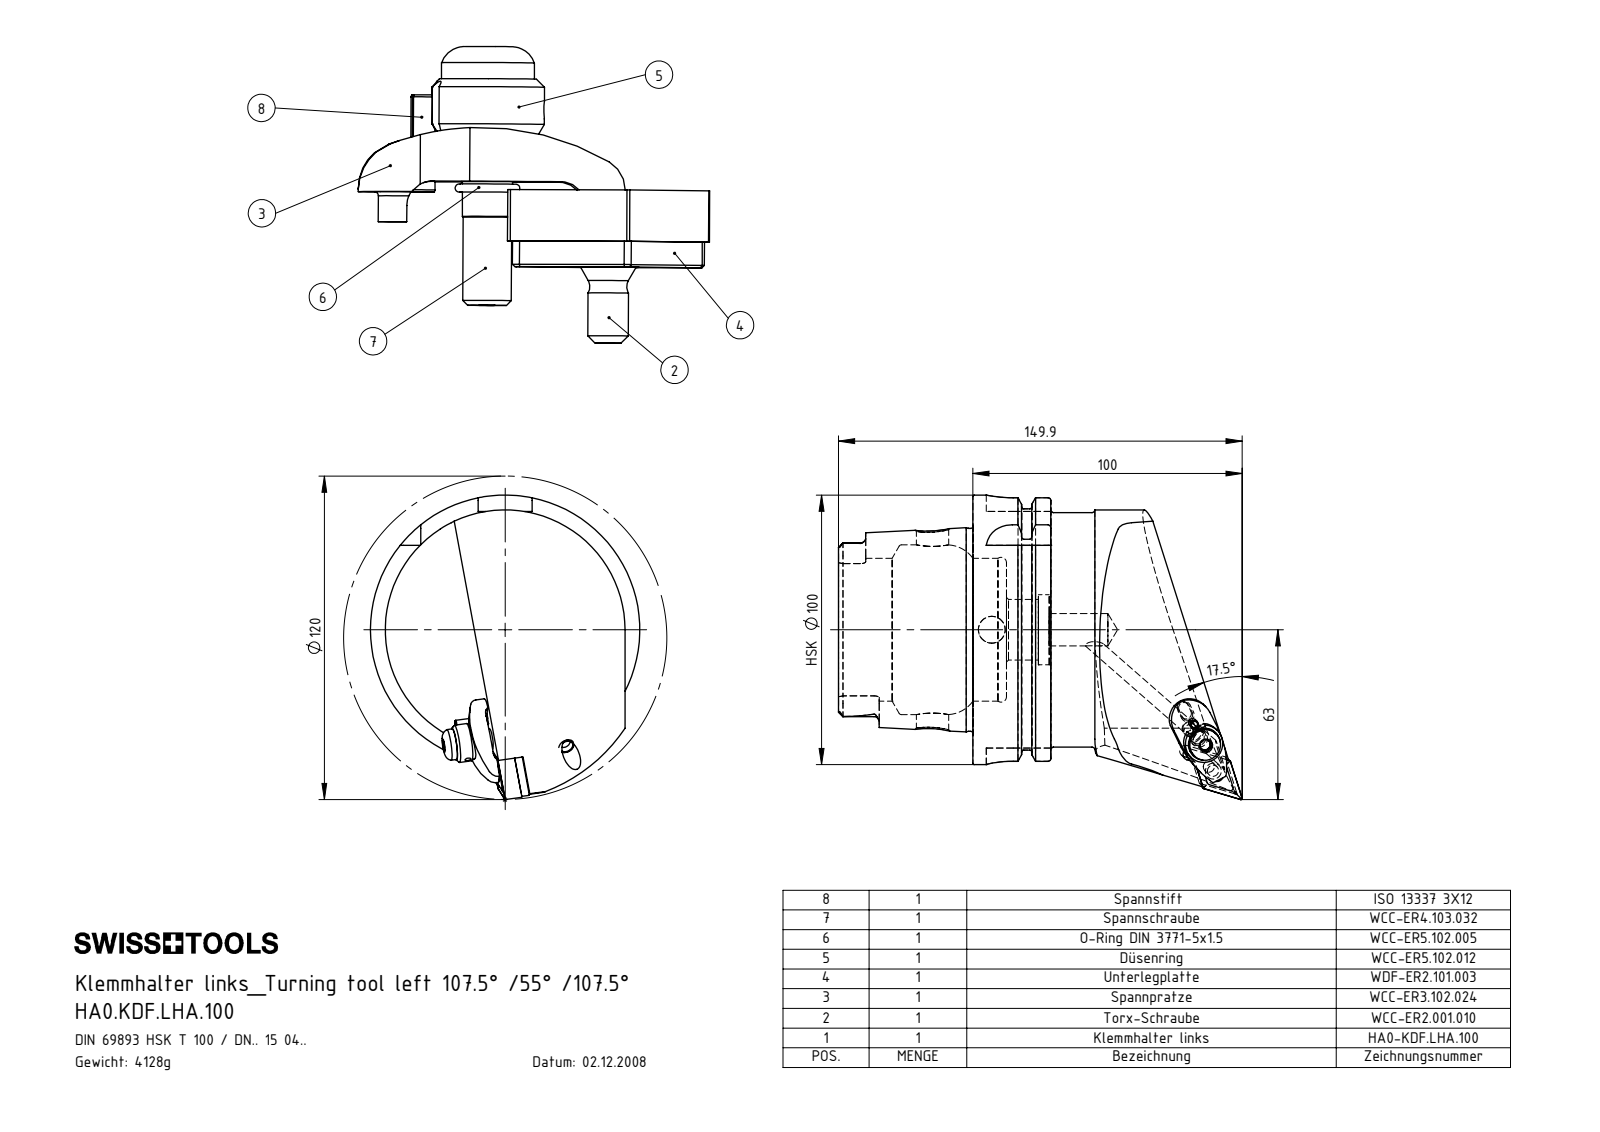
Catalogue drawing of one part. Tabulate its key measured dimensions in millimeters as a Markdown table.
| quantity | value |
| --- | --- |
| part name | ISO 13337 - 3 x 12_PreviewCfg; WDF-ER2.101.003_A; WCC-ER3.102.024_C; WCC-ER2.001.010_A (+7 more) |
| STEP written by | SolidWorks 2017 (AUTOMOTIVE_DESIGN) |
| units | millimeters |
| bodies | 11 solids, 465 faces (120 planar, 154 cylindrical, 191 other) |
| overall size | 149.9 × 113 × 100 |
| volume | 526 872 mm³ |
| surface area | 72 766 mm² |
| round holes (diameter × count) | 2 × 3, 5 × 3, 7 × 2, 12 × 2, 2.4 × 1, 3 × 1, 4.2 × 1, 5.16 × 1, 6 × 1, 6.2 × 1, 6.5 × 1, 8.5 × 1 |
| round bosses / shafts (diameter × count) | 6 × 2, 3 × 2, 100 × 1, 91.95 × 1, 87 × 1, 75.26 × 1, 14 × 1, 11.5 × 1 |
| partial cylindrical surfaces (radius × count) | 0.39 × 6, 0.69 × 6, 1.9 × 6, 0.4 × 5, 10 × 4, 1.5 × 3, 2 × 2, 3 × 2 |
| main face-to-face distances | 12.45, 28.95, 16.5, 49.9, 62.35, 78.85, 87.8, 78.2, 28.3, 15.85 |
| hole center spacings | 8, 15, 23, 8.2, 14.8 |
